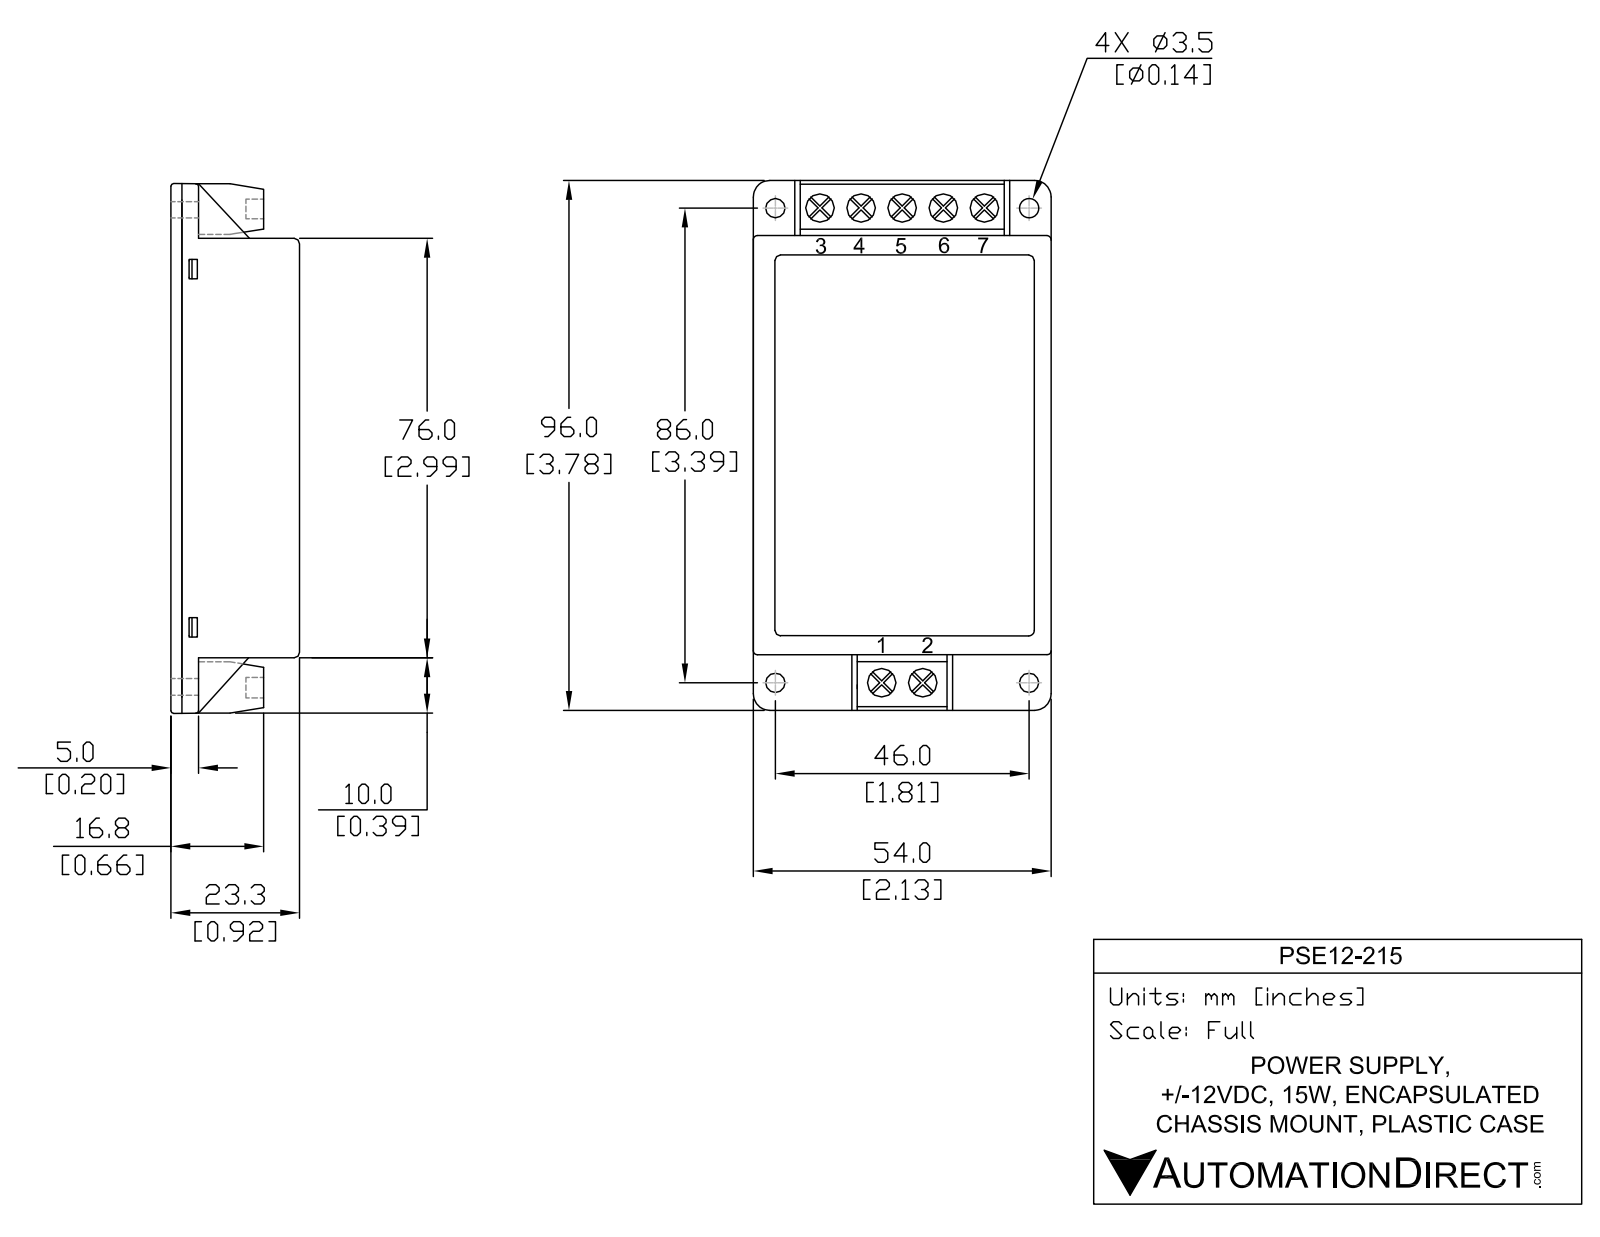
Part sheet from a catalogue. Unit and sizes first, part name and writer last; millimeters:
Units: millimetres
Overall size (bounding box): 96 × 54.1 × 23.4
Round holes (diameter × count): ⌀5.1 ×7, ⌀3.6 ×4
Partial cylindrical surfaces — rounded edges, fillets, slot ends (radius × count): R0.8 ×20, R3.2 ×4
Main face-to-face distances: 2, 2, 21.3, 23.3, 21.3, 54.1, 75.9, 23.4, 21.4, 0.4
Hole centre spacings: 6.6, 13.2, 6.6, 19.7, 26.3, 46, 85.4, 85.4
Volume: 105 900 mm³ · Surface area: 29 380 mm²
Bodies: 2 solids, 369 faces (246 planar, 62 cylindrical, 61 other)
Part name (STEP PRODUCT): PSE12-215
STEP written by: SolidWorks 2011 (CONFIG_CONTROL_DESIGN)
